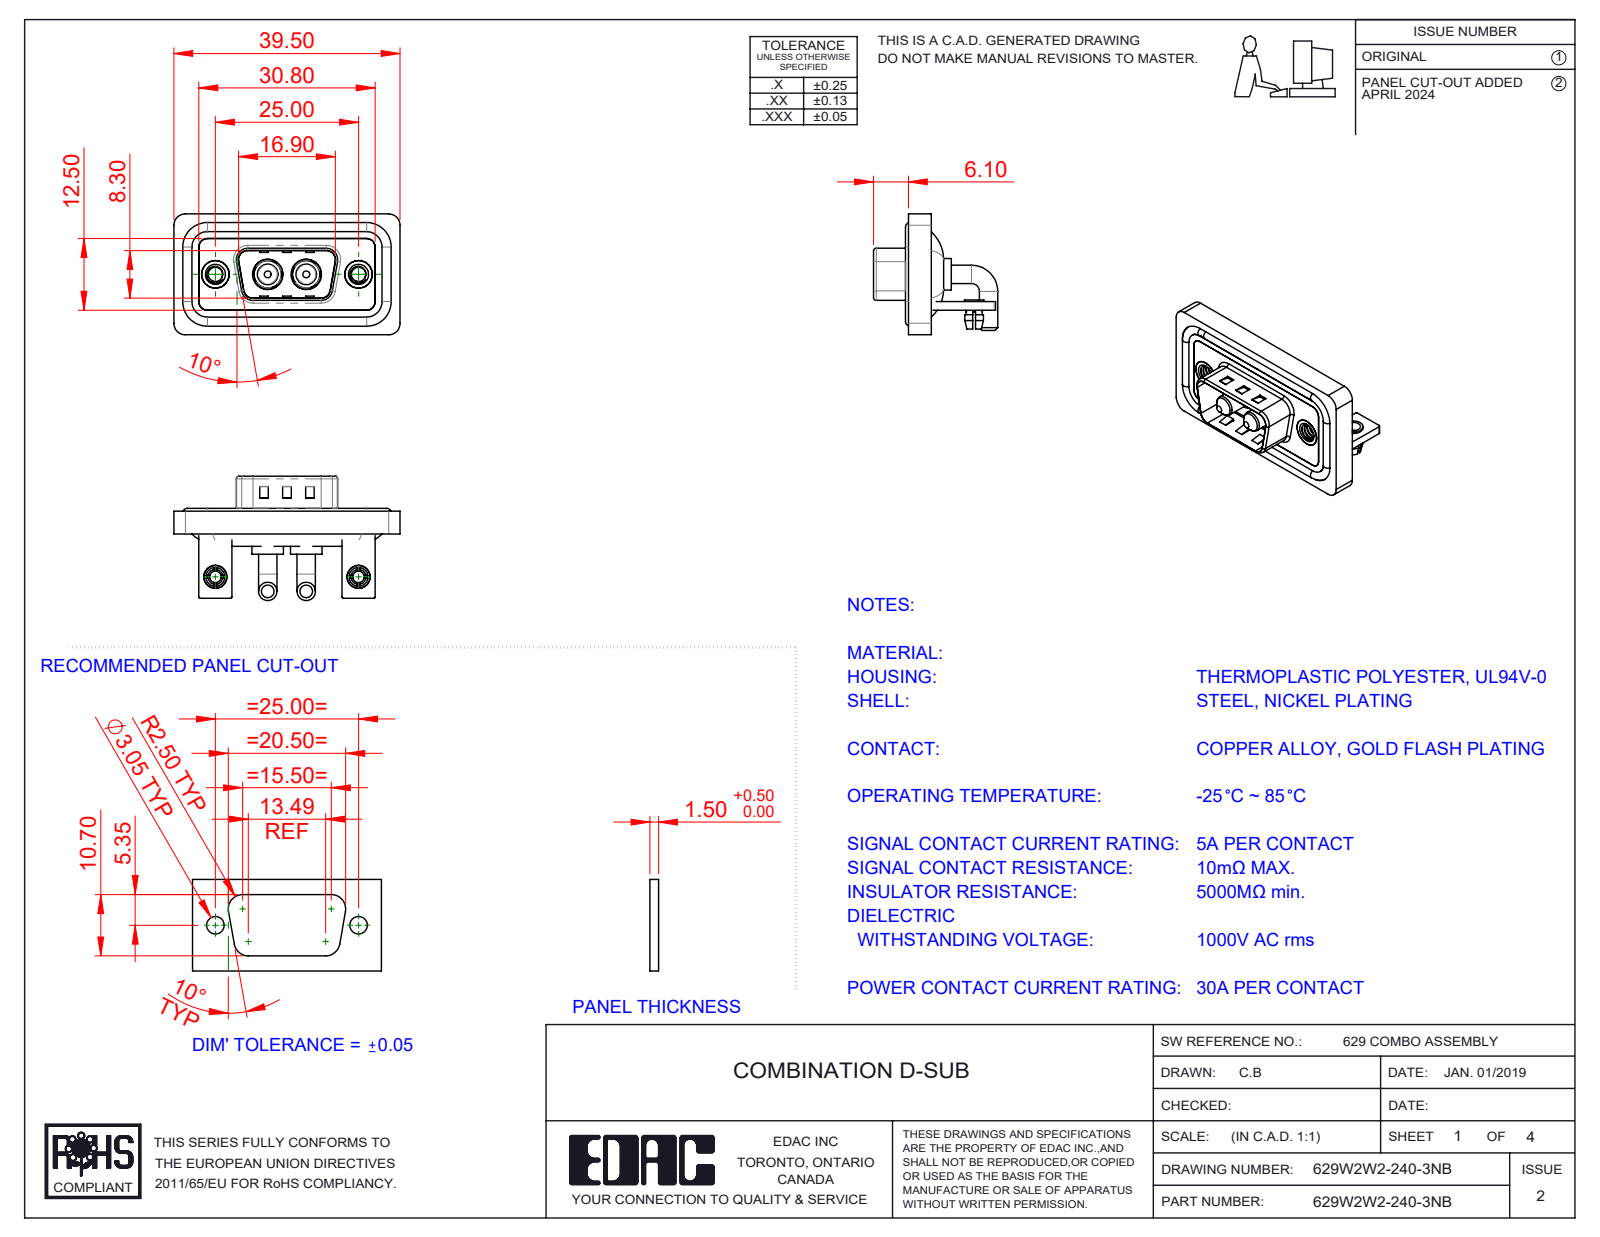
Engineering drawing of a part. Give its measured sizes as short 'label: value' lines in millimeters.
name: 629Combo Shell Front_09 Contacts; 629Combo Waterproof Housing_09 Contacts; 629Combo Shell Rear_09 Contacts; 629Combo Housing_2W2 (+5 more)
written by: SolidWorks 2023 (CONFIG_CONTROL_DESIGN)
unit: mm
bodies: 15 solids, 627 faces (233 planar, 272 cylindrical, 122 other)
size: 39.5 × 21.7 × 21.1
volume: 4 949 mm³; area: 8 003 mm²
holes: 4× ⌀2.5, 2× ⌀2, 2× ⌀3.2, 2× ⌀4, 2× ⌀4.8, 2× ⌀4.85, 2× ⌀5, 2× ⌀5.3
bosses: 4× ⌀3.2, 4× ⌀1.6, 2× ⌀5.5, 2× ⌀5.2, 2× ⌀4.9, 2× ⌀4.75, 2× ⌀4, 2× ⌀3.75
rounds: 19× R2, 18× R1.5, 16× R0.25, 9× R0.5, 8× R1.6, 4× R0.6, 4× R0.65, 4× R0.9
face distances: 0.4, 1.5, 2.9, 0.8, 1.1, 1.2, 2.1, 1.6, 3.7, 2.5
hole spacings: 9.14, 15.86, 25, 6.72
